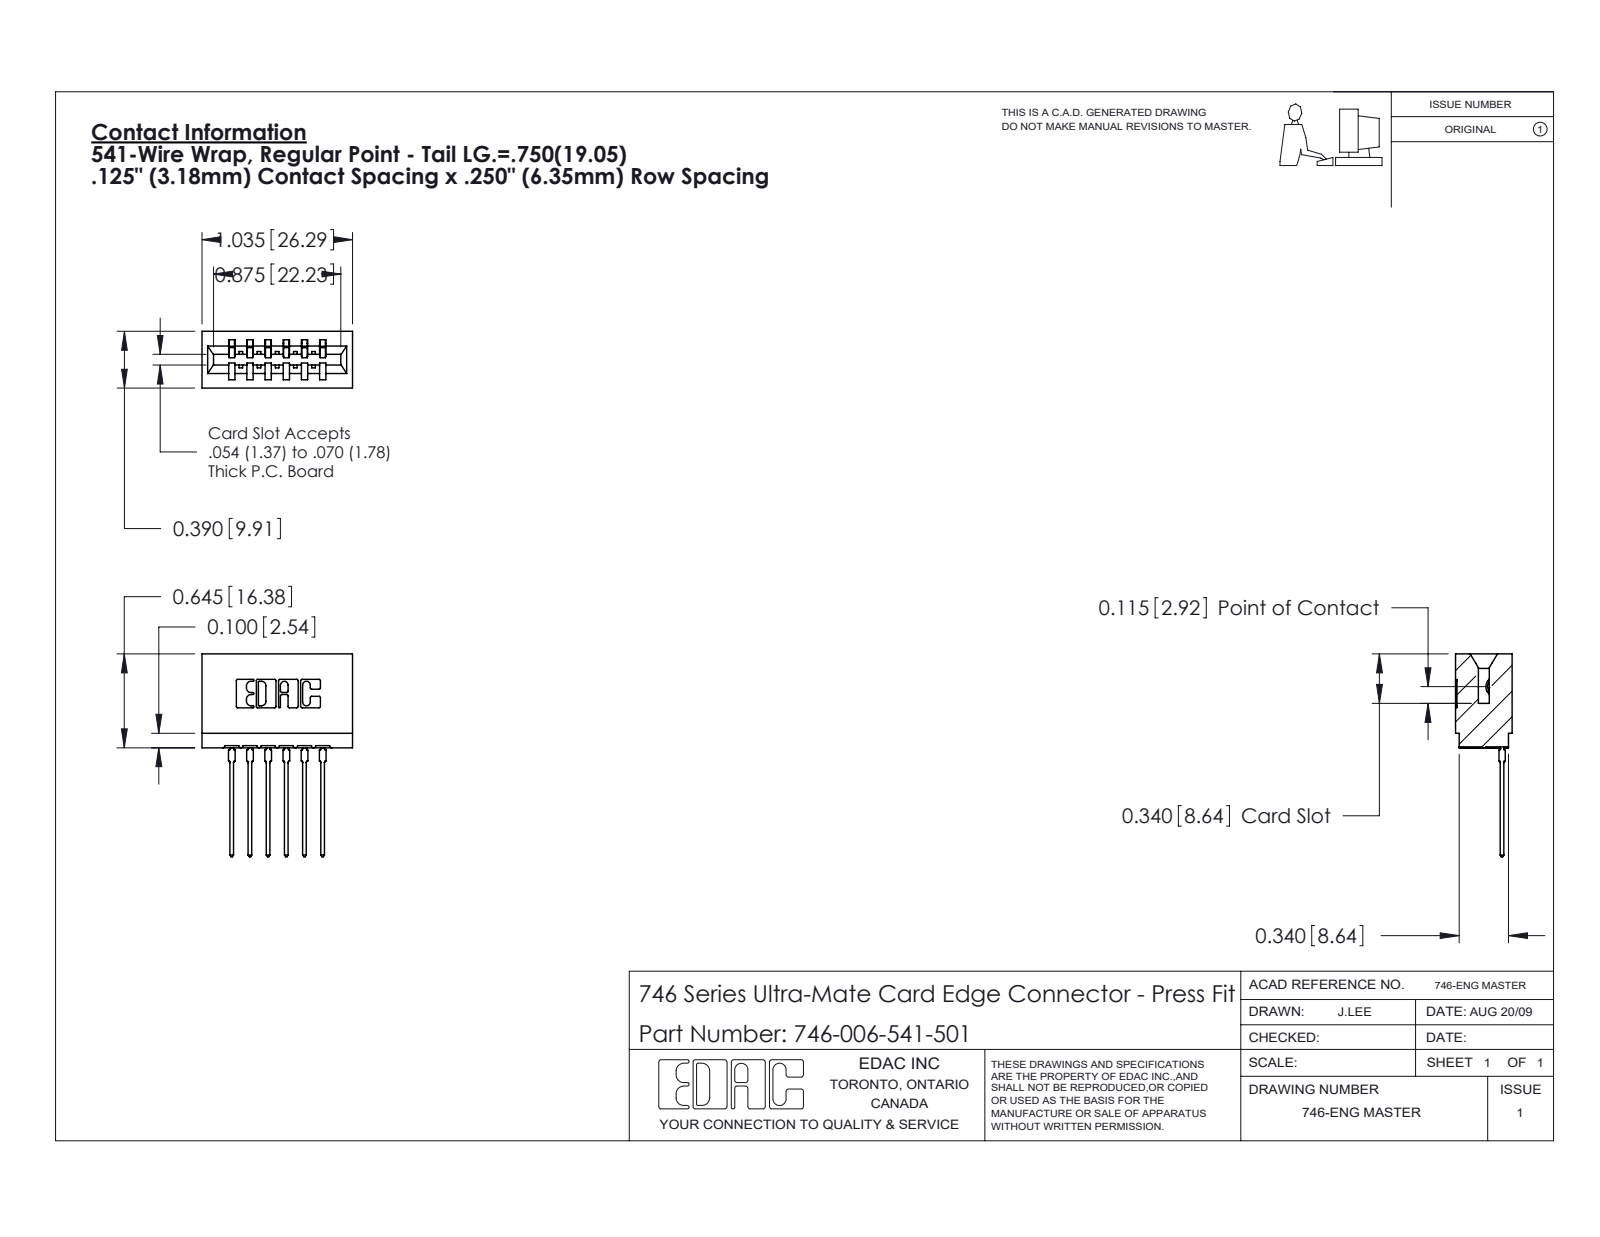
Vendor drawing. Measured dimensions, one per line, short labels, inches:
name: 746 Part_.340 Slot Depth - 01; 746-006-541-501; 746-292-001_541
written by: SolidWorks 2020 (CONFIG_CONTROL_DESIGN)
unit: in
bodies: 7 solids, 745 faces (433 planar, 156 cylindrical, 156 other)
size: 1.394 × 1.035 × 0.39
volume: 0.195 in³; area: 6.066 in²
rounds: 22× R0.01, 12× R0.021, 7× R0.015, 6× R0.007, 6× R0.031, 4× R0.005, 4× R0.011, 3× R0.026
face distances: 0.25, 0.125, 0.042, 0.333, 0.057, 0.375, 0.39, 0.292, 0.5, 0.208
